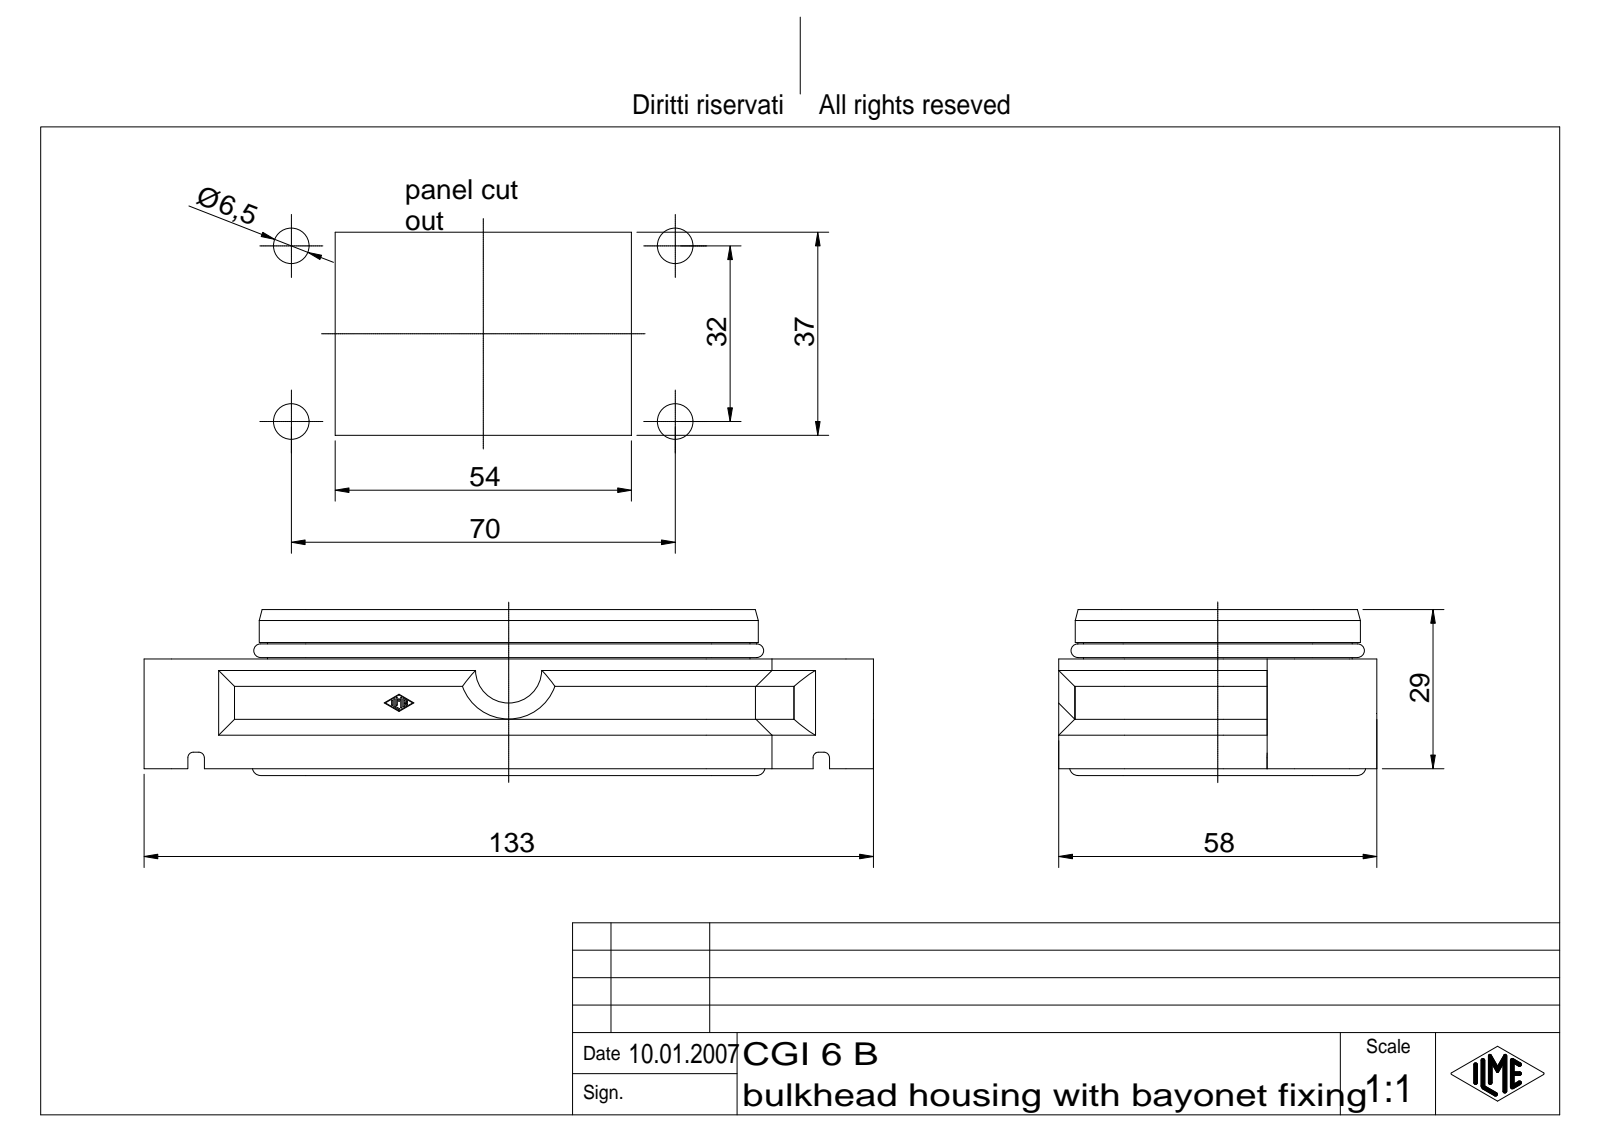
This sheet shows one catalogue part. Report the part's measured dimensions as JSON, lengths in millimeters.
{"part_name": "Anbaugehäuse", "step_written_by": "Autodesk Inventor 7 (AUTOMOTIVE_DESIGN)", "units": "millimeters", "bodies": {"solids": 1, "faces": 360, "planar": 176, "cylindrical": 134, "other": 50}, "overall_size": [133, 58, 30.25], "volume_mm3": 59467, "surface_area_mm2": 32629, "round_holes": [[5.5, 4], [3.24, 2]], "round_bosses_or_shafts": [[2.5, 4], [3, 2]], "partial_cylinders_radius": [[0.1, 14], [5, 8], [7, 6], [1, 4], [3.25, 4], [6.5, 4], [8.5, 4], [9.5, 4]], "face_to_face_distances": [3, 6.5, 45, 51.5, 20, 3.5, 9, 48.5, 55, 5.5], "hole_center_spacings": [16.03, 71.81, 32, 71, 77.88, 69]}
